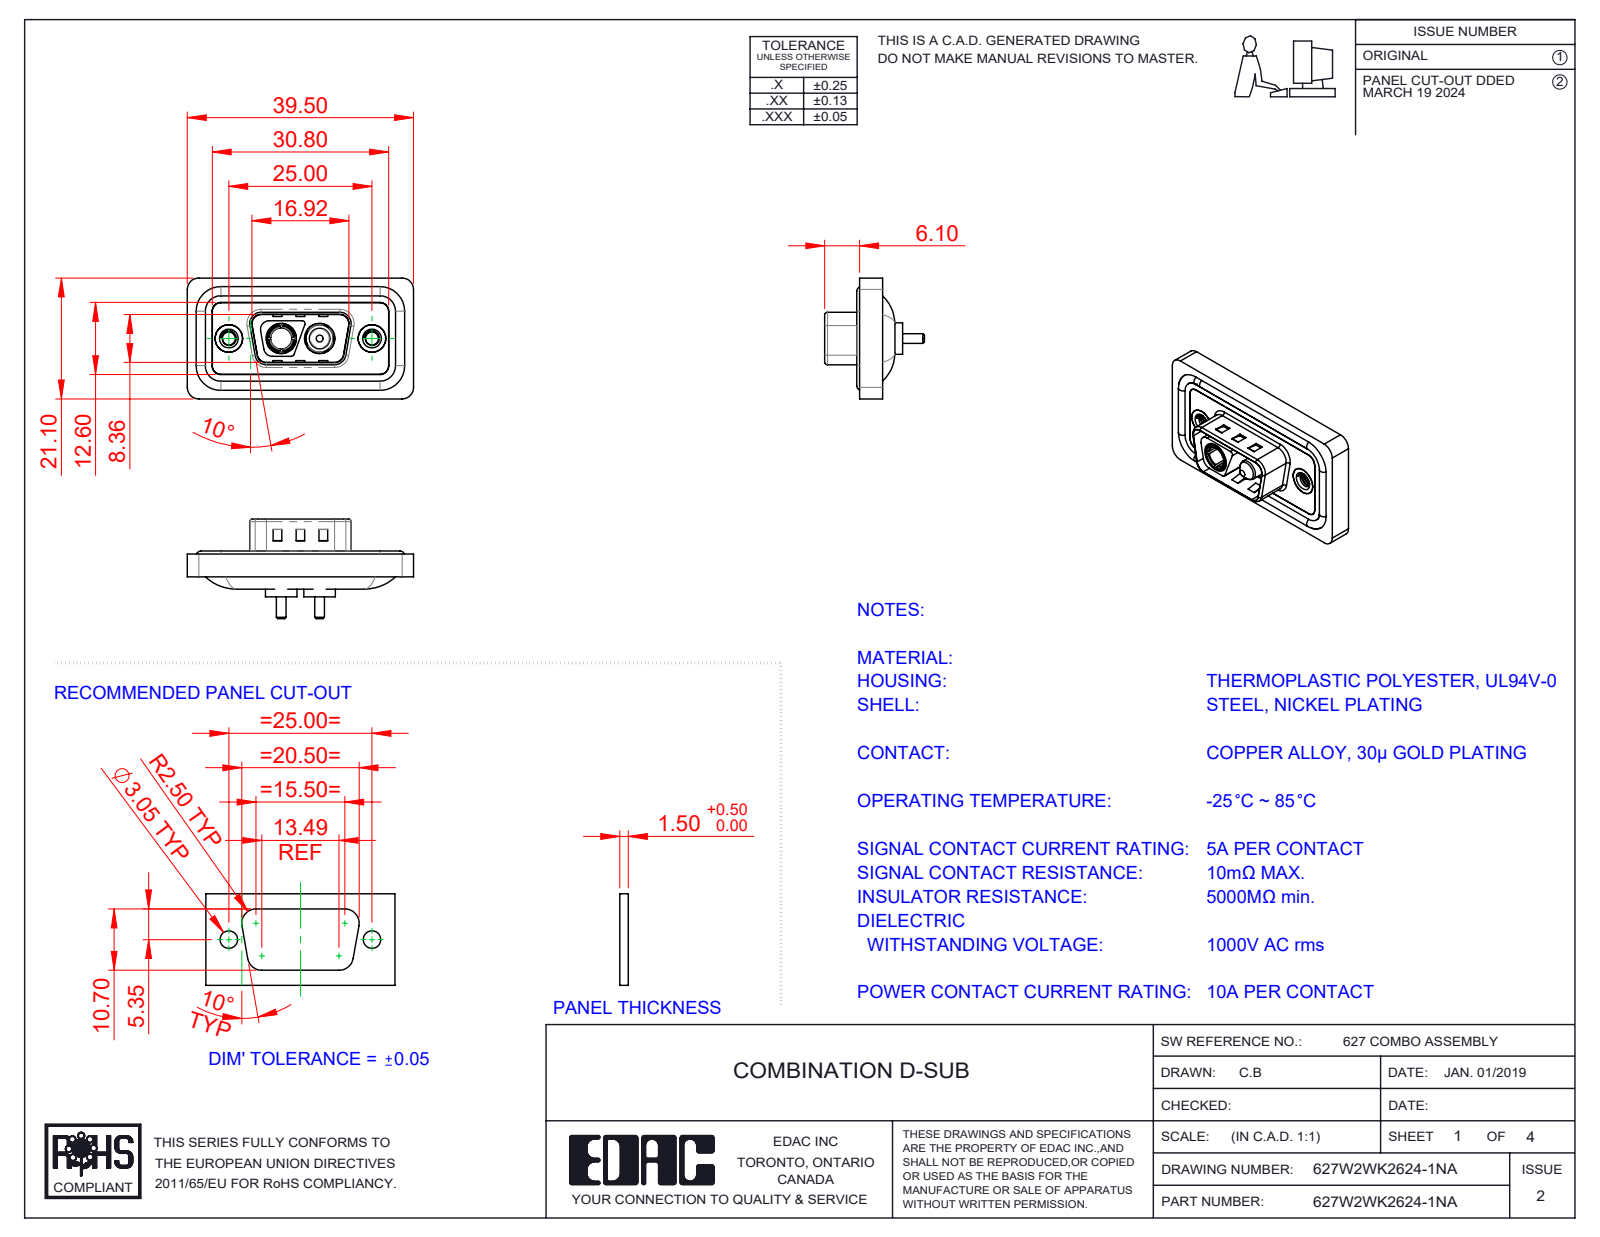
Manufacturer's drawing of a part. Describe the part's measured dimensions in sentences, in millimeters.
The part is named "627Combo Shell Front_09 Contacts; 627Combo Shell Rear_09 Contacts; 627Combo Housing_2WK2; Power Socket_10A S (+4 more)". Its 3-D file was written by "SolidWorks 2023 (CONFIG_CONTROL_DESIGN)". It is 11 solids with 532 faces: 189 planar, 229 cylindrical and 114 other. Overall it measures 39.5 by 21.1 by 17.4 millimeters. Its volume is 4 526 cubic millimeters and its surface area 7 315 square millimeters. Round holes: 2 of diameter 2.26, 2 of diameter 4, 2 of diameter 4.8, 2 of diameter 4.85, 2 of diameter 5, 2 of diameter 5.3, 1 of diameter 3.7. Round bosses or shafts: 4 of diameter 1.6, 2 of diameter 5.5, 2 of diameter 5.2, 2 of diameter 4.9, 2 of diameter 4.75, 2 of diameter 3.75, 2 of diameter 1.7, 1 of diameter 4.96. Partial cylindrical surfaces (rounded edges, fillets, slot ends): 24 of radius 1.5, 18 of radius 2, 10 of radius 0.5, 8 of radius 1.6, 4 of radius 0.25, 4 of radius 0.6, 4 of radius 0.65, 4 of radius 0.9. The main face-to-face distances are 0.4, 1.1, 2.9, 0.5, 3.1, 1.6, 1.5, 4, 2.5, 1.8. The hole center spacings are 9.14, 15.86, 6.72, 25.
